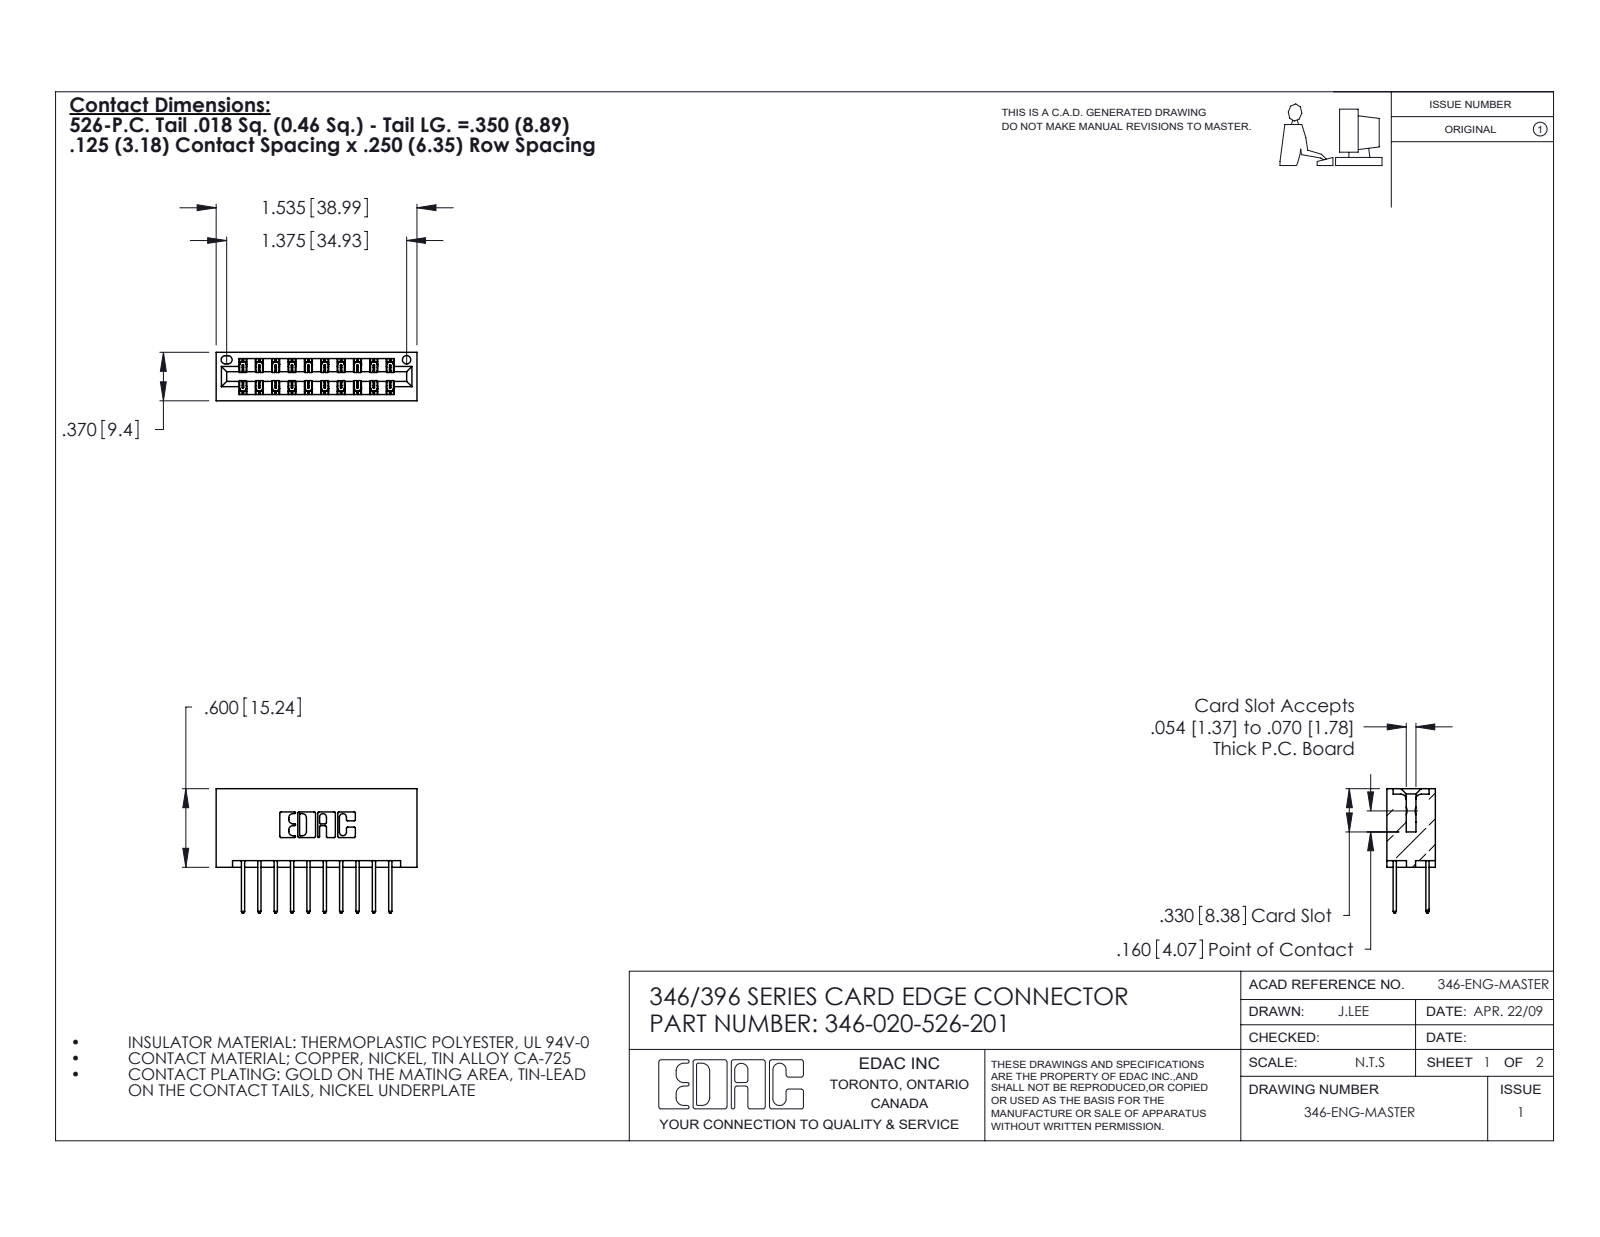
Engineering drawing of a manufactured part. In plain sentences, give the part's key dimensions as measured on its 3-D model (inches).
The part is named "346 Part_No Mounting Lugs; 346-020-526-201; 345-292-001_345-293-126". Its 3-D file was written by "SolidWorks 2020 (CONFIG_CONTROL_DESIGN)". It is 21 solids with 1154 faces: 772 planar, 382 cylindrical and 0 other. Overall it measures 1.535 by 0.95 by 0.37 inches. Its volume is 0.254 cubic inches and its surface area 8.563 square inches. Round holes: 1 of diameter 0.064. Partial cylindrical surfaces (rounded edges, fillets, slot ends): 30 of radius 0.006, 22 of radius 0.01, 20 of radius 0.01, 6 of radius 0.007, 6 of radius 0.031, 3 of radius 0.026, 2 of radius 0.014, 2 of radius 0.022. The main face-to-face distances are 0.25, 0.048, 0.322, 0.37, 0.072, 0.298, 0.025, 0.275, 0.5, 0.148.
